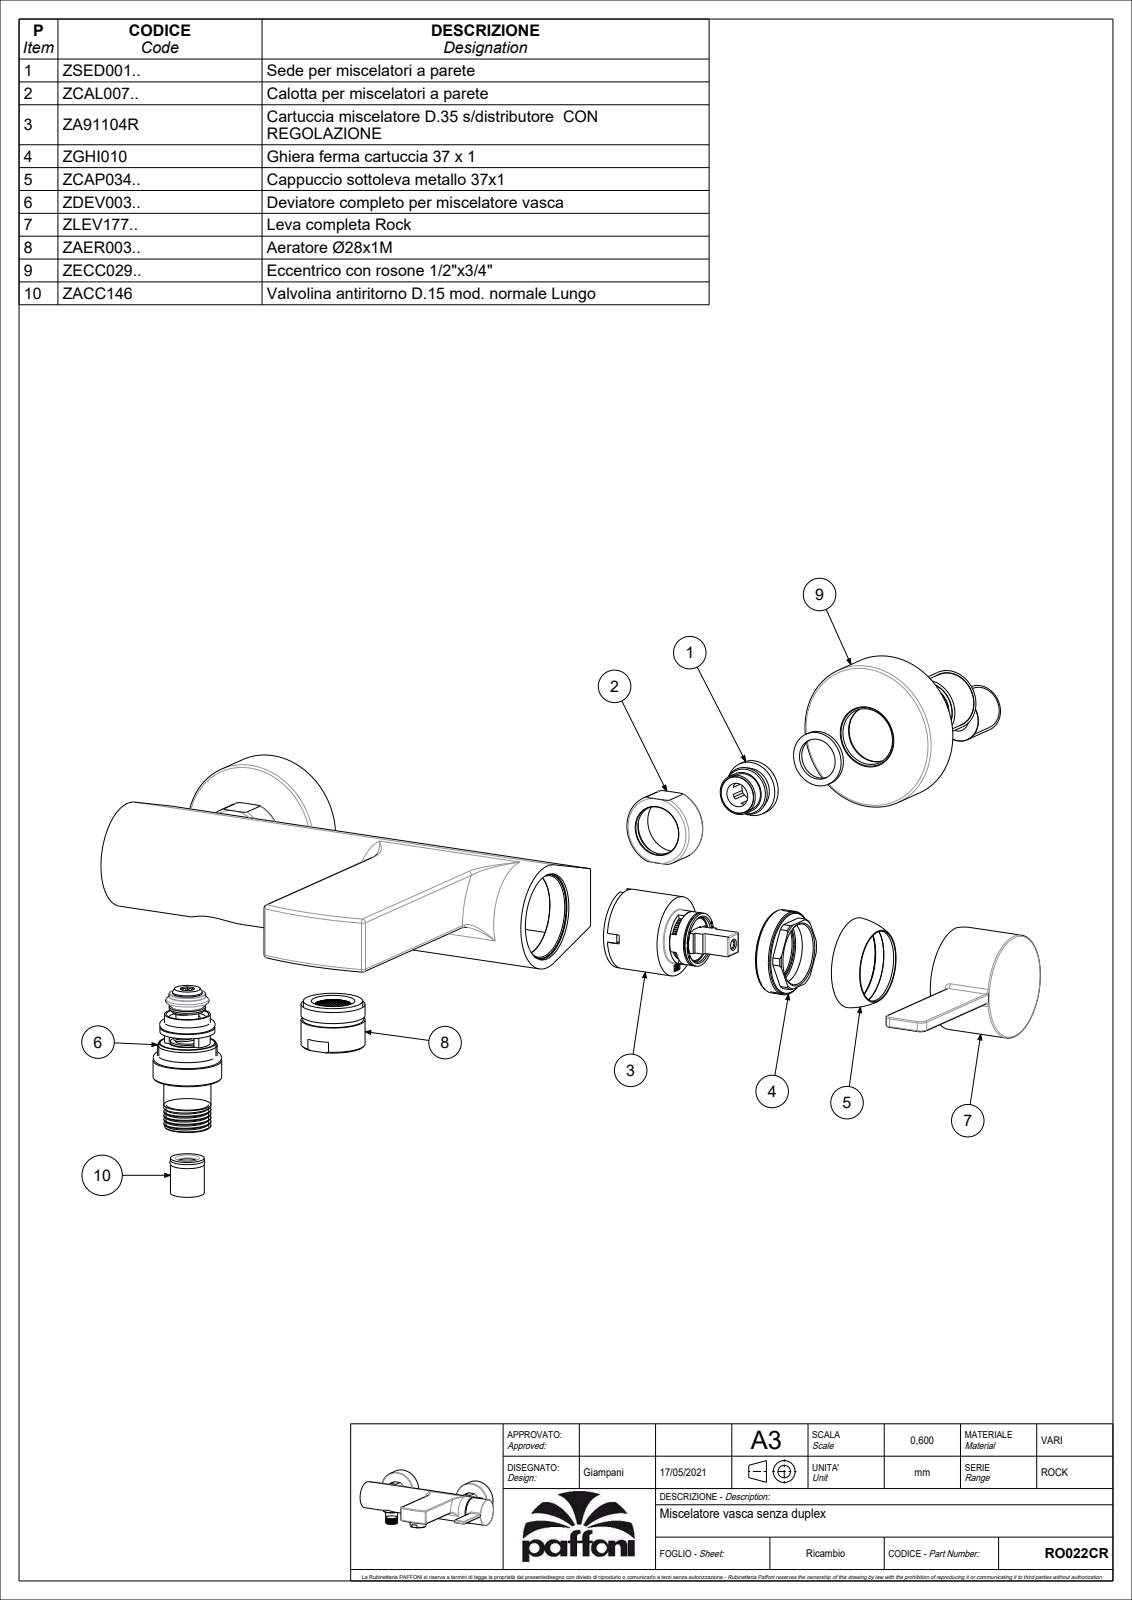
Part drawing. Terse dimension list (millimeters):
name: RO022CR
written by: CREO PARAMETRIC BY PTC INC, 2020044 (CONFIG_CONTROL_DESIGN)
unit: mm
bodies: 2 solids, 1409 faces (1105 planar, 170 cylindrical, 134 other)
size: 244.35 × 195.5 × 76.75
volume: 434 192 mm³; area: 177 175 mm²
holes: 2× ⌀10.5, 2× ⌀16.5, 2× ⌀21, 1× ⌀3, 1× ⌀3.5, 1× ⌀4.2, 1× ⌀7, 1× ⌀8.5, 1× ⌀9, 1× ⌀11, 1× ⌀14, 1× ⌀15.1
bosses: 3× ⌀24, 2× ⌀63.5, 1× ⌀45.5, 1× ⌀37, 1× ⌀30, 1× ⌀28, 1× ⌀27, 1× ⌀26
rounds: 9× R0.5, 8× R1.5, 2× R0.3, 2× R2, 2× R3, 2× R15.6, 1× R3.5, 1× R9.5
face distances: 3.5, 3, 31.5, 20.5, 34.5, 48.5, 19, 15.5, 47.5, 20
hole spacings: 6, 51.6, 150, 154.02, 201.6
